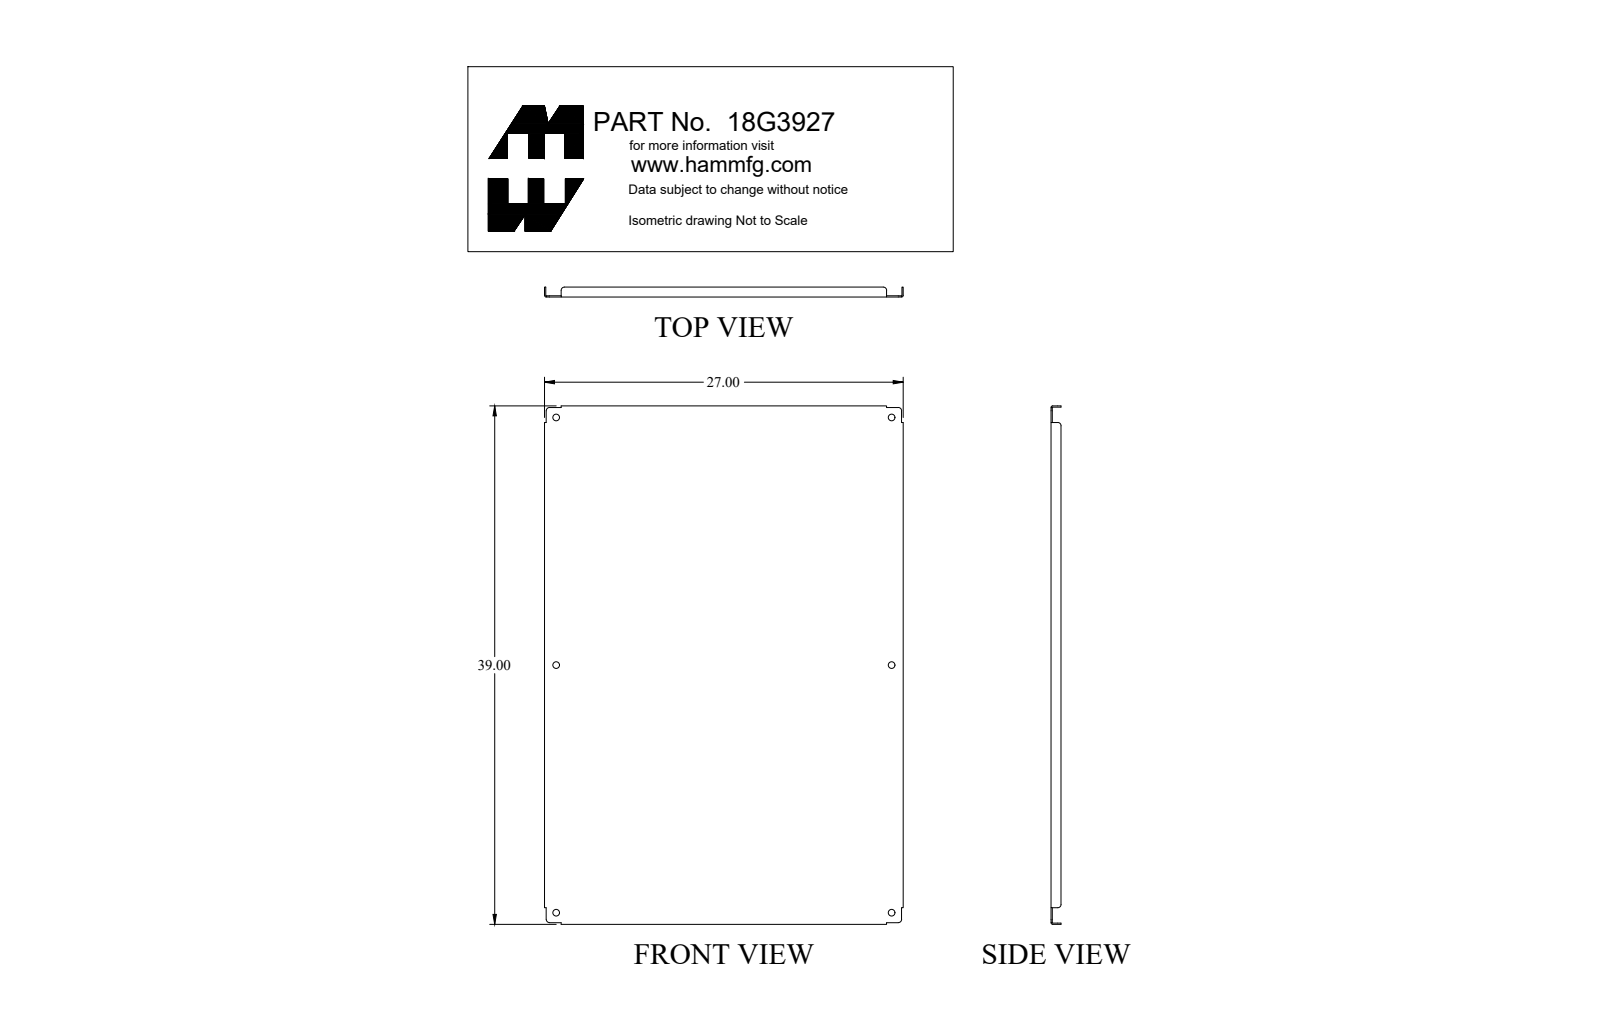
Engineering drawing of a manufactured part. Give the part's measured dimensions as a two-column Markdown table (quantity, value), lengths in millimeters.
| quantity | value |
| --- | --- |
| part name | 18G3927_Default |
| STEP written by | SolidWorks 2018 (CONFIG_CONTROL_DESIGN) |
| units | millimeters |
| bodies | 1 solid, 62 faces (30 planar, 32 cylindrical, 0 other) |
| overall size | 990.6 × 685.8 × 19.1 |
| volume | 1 753 000 mm³ |
| surface area | 1 462 000 mm² |
| round holes (diameter × count) | 12.7 × 6 |
| partial cylindrical surfaces (radius × count) | 6.4 × 8, 0.8 × 4, 3.2 × 4 |
| main face-to-face distances | 2.4, 683.4, 988.2, 681, 685.8, 990.6, 985.8, 19.1, 16.6, 3.2 |
| hole center spacings | 473.1, 797, 641.4, 946.2, 1143 |
